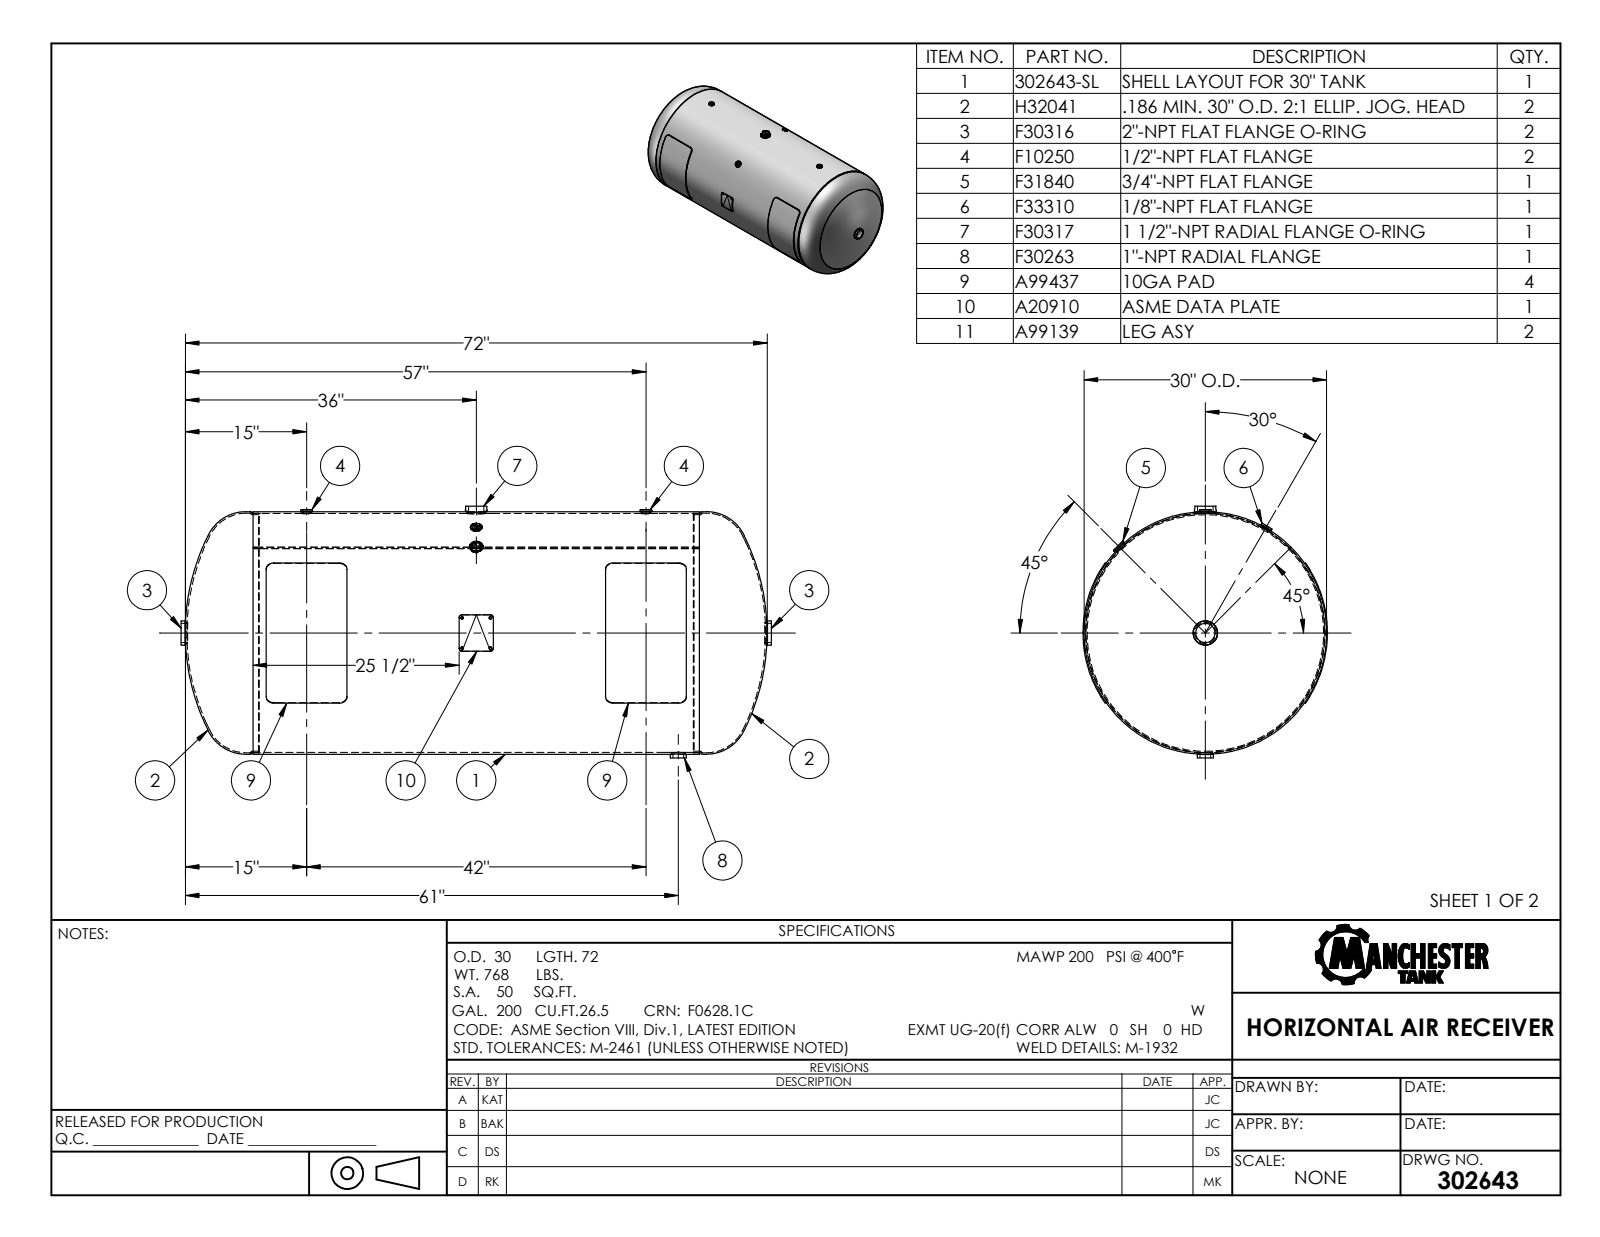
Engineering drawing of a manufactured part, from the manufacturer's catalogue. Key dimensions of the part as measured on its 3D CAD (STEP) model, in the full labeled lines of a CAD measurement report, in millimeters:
Part name (STEP PRODUCT): 302643
STEP written by: SolidWorks 2022 (AUTOMOTIVE_DESIGN)
Units: millimetres
Bodies: 30 solids, 628 faces (270 planar, 190 cylindrical, 168 other)
Overall size (bounding box): 1856.1 × 1079.2 × 889.1
Volume: 42 440 000 mm³ · Surface area: 16 140 000 mm²
Round holes (diameter × count): ⌀21.3 ×2, ⌀10.3 ×1, ⌀26.7 ×1, ⌀33.4 ×1, ⌀48.3 ×1, ⌀60.3 ×1, ⌀743.1 ×1, ⌀750.5 ×1, ⌀752.6 ×1, ⌀762 ×1
Round bosses / shafts (diameter × count): ⌀36.8 ×3, ⌀36.5 ×3, ⌀27 ×2, ⌀752.6 ×1, ⌀76.2 ×1, ⌀68.3 ×1, ⌀66.7 ×1, ⌀57.6 ×1
Partial cylindrical surfaces — rounded edges, fillets, slot ends (radius × count): R3.2 ×16, R6.4 ×12, R9.5 ×12, R7.1 ×8, R10.7 ×8, R12 ×4, R385.7 ×2, R177.8 ×1
Main face-to-face distances: 4.4, 5.7, 911.4, 1066.8, 224.2, 915.7, 10.1, 917, 921.4, 228.6
Hole centre spacings: 533.4, 101.6, 635, 1066.8, 1168.4
